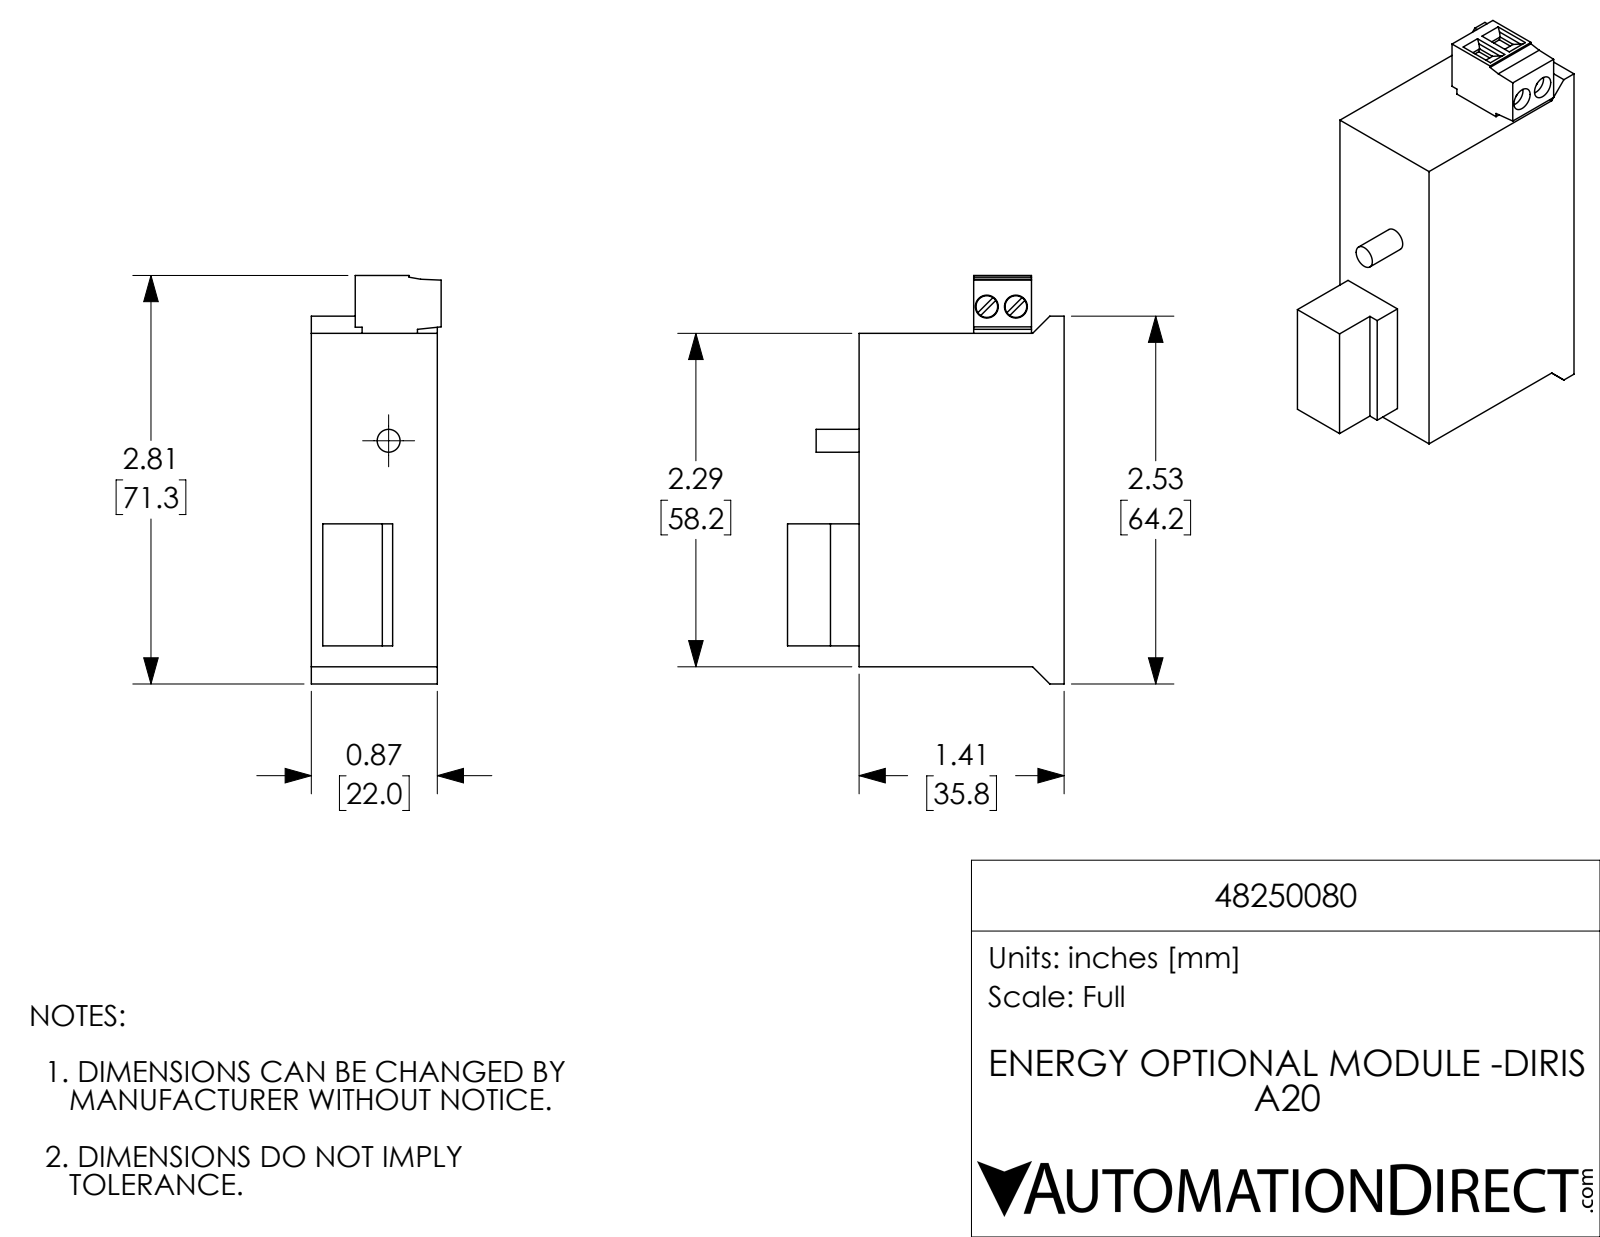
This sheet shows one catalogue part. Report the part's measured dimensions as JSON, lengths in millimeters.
{"part_name": "48250080", "step_written_by": "SolidWorks 2017 (AUTOMOTIVE_DESIGN)", "units": "millimeters", "bodies": {"solids": 1, "faces": 78, "planar": 66, "cylindrical": 12, "other": 0}, "overall_size": [71.3, 48.3, 22.7], "volume_mm3": 50720, "surface_area_mm2": 10230, "round_holes": [[4, 3]], "round_bosses_or_shafts": [[3.8, 2]], "face_to_face_distances": [22, 35.8, 58.2, 2, 20, 48.3, 12.5, 12.4, 10.4, 9.6], "hole_center_spacings": [5.1]}
